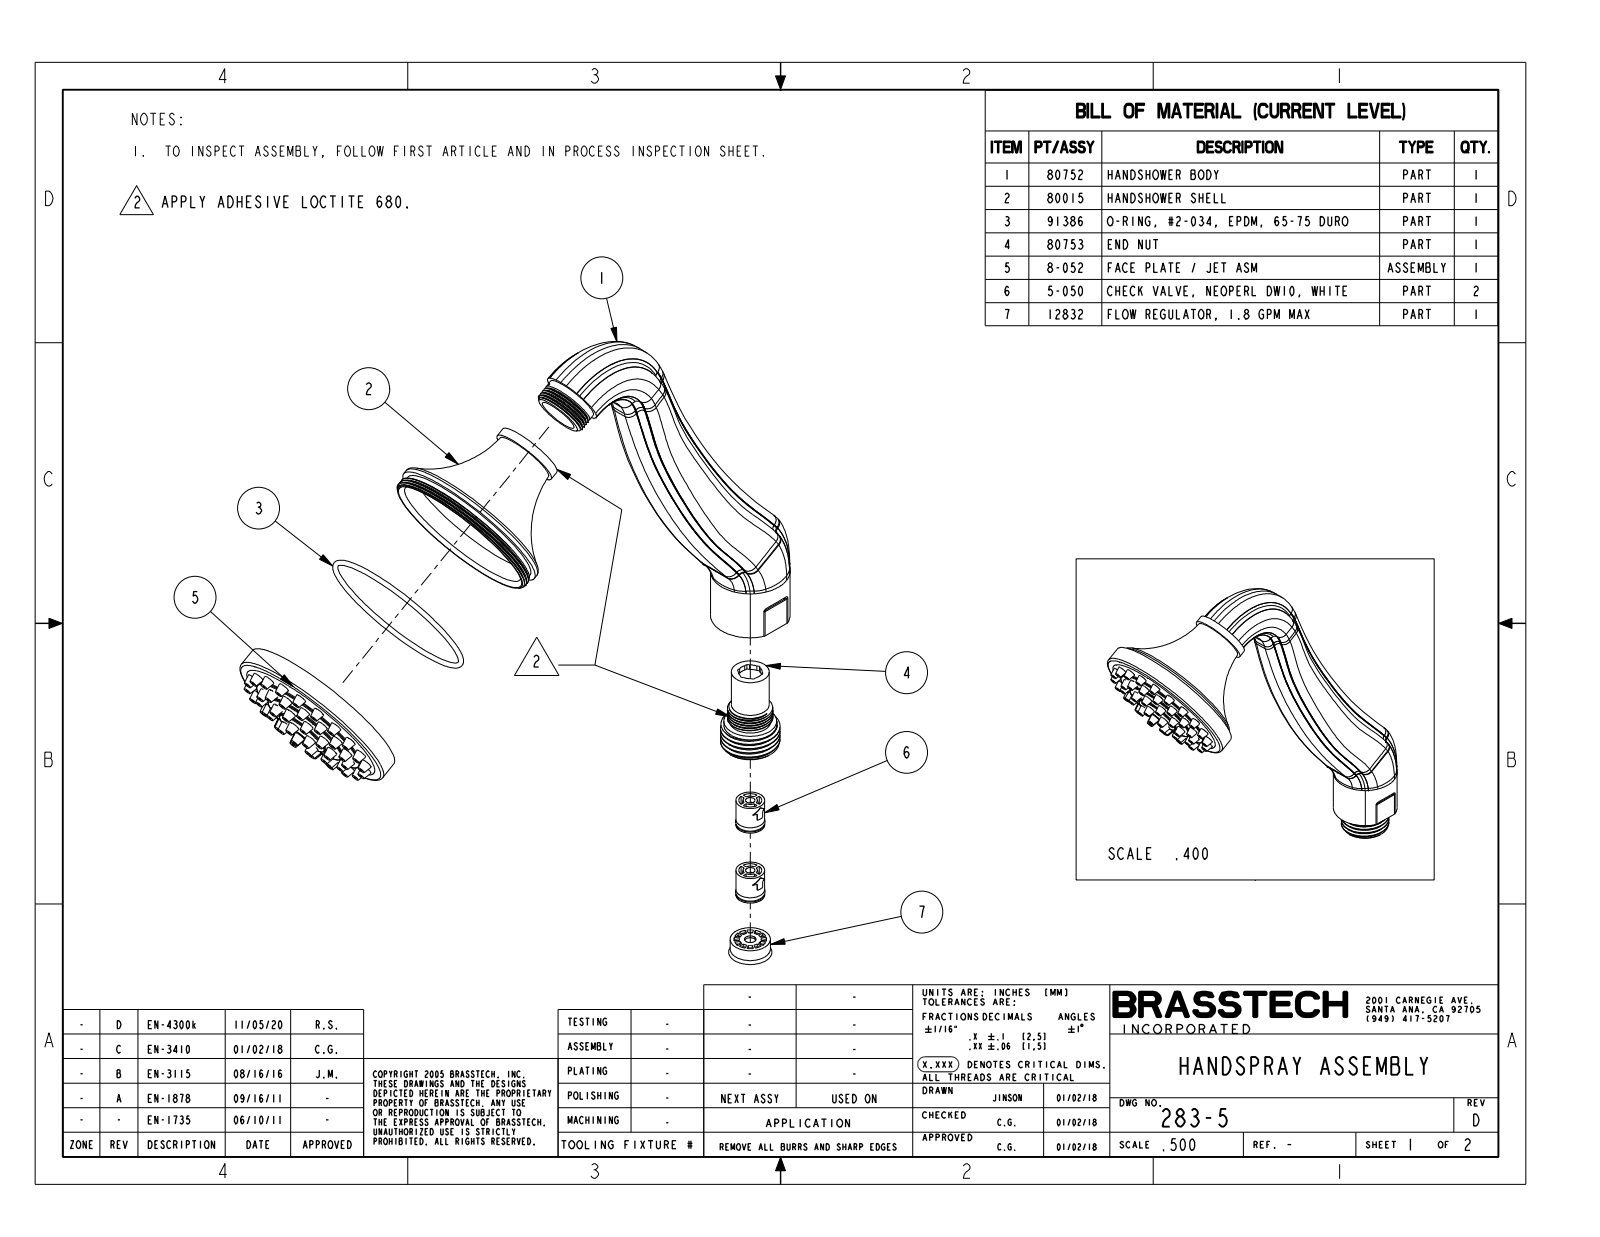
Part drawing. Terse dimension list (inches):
name: 80752
written by: CREO PARAMETRIC BY PTC INC, 2018400 (CONFIG_CONTROL_DESIGN)
unit: in
bodies: 1 solid, 959 faces (164 planar, 280 cylindrical, 515 other)
size: 8.157 × 3.377 × 2.49
volume: 9.344 in³; area: 45.18 in²
holes: 51× ⌀0.039, 51× ⌀0.079
bosses: 1× ⌀2.49, 1× ⌀2.3, 1× ⌀1.79, 1× ⌀1.29, 1× ⌀0.95, 1× ⌀0.818, 1× ⌀0.79, 1× ⌀0.725
rounds: 50× R0.065, 2× R0.05, 1× R0.547
face distances: 0.275, 0.39, 0.07, 0.06, 0.069, 0.122, 1, 0.053, 0.422, 0.147
hole spacings: 0.312, 0.61, 1.115, 1.299, 1.427, 0.882, 0.313, 0.618
